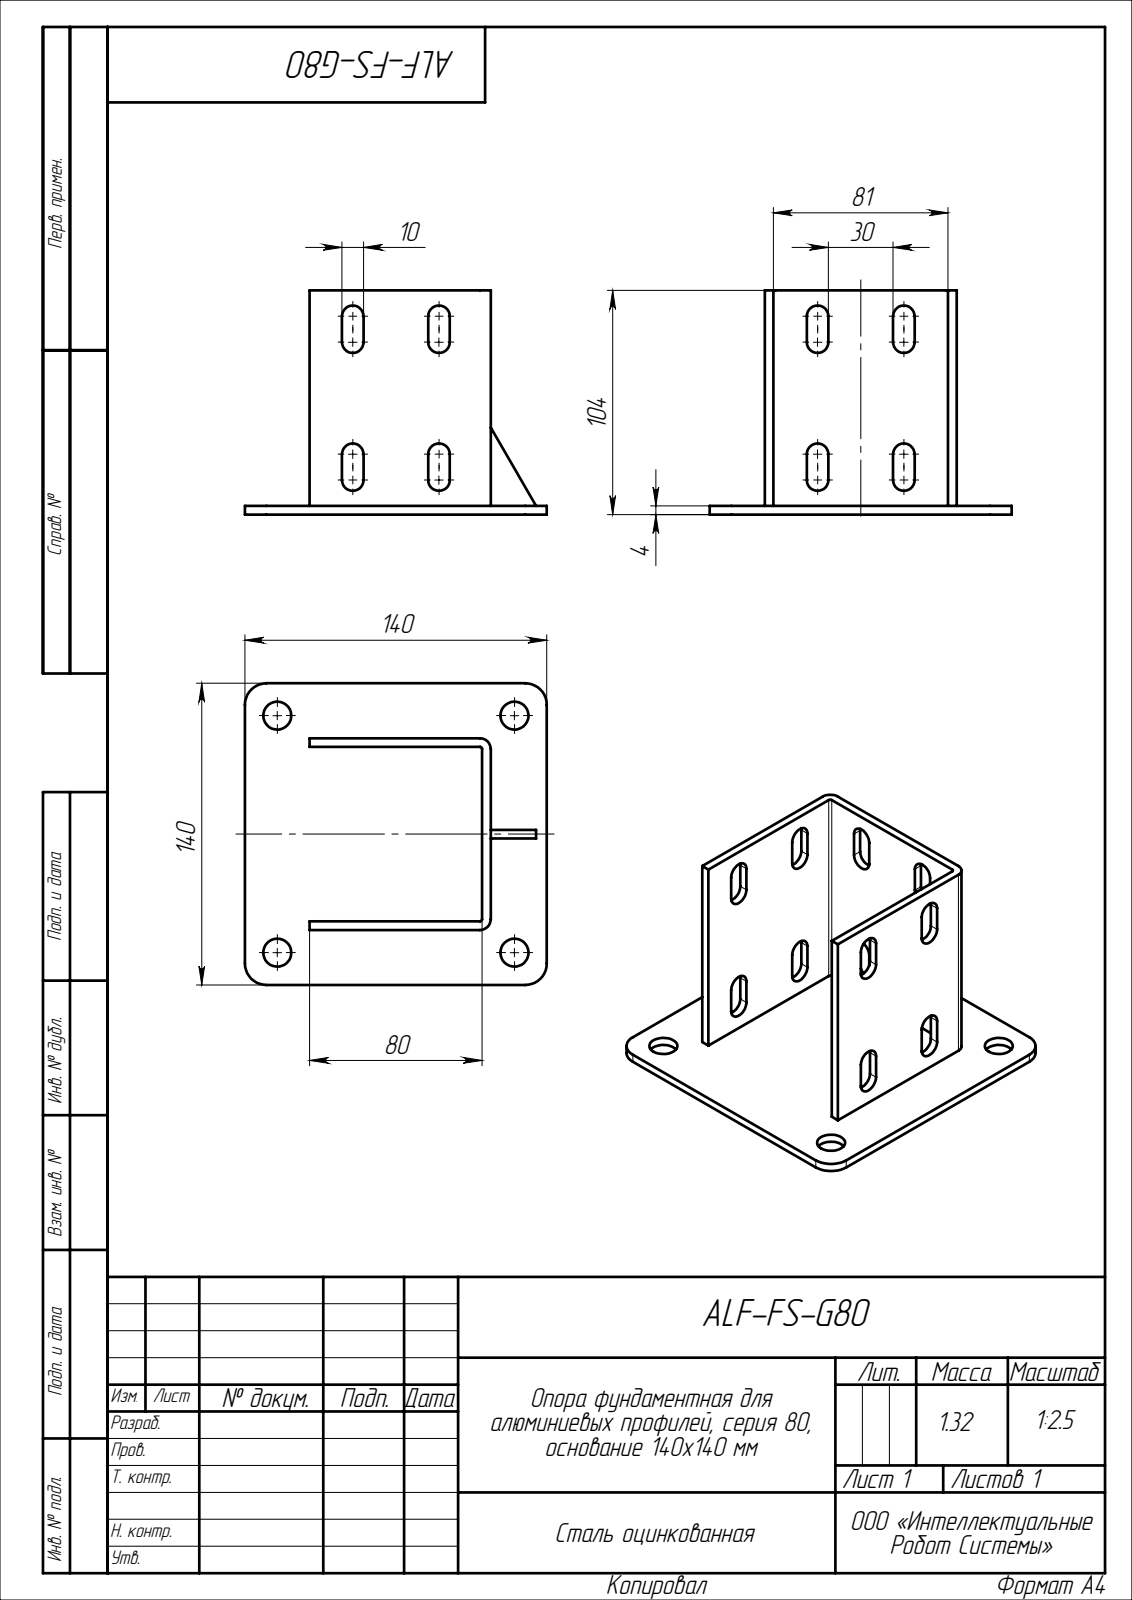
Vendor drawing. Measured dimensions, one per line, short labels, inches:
name: ALF-FS-G80
written by: SolidWorks 2022 (CONFIG_CONTROL_DESIGN)
unit: in
bodies: 1 solid, 82 faces (42 planar, 40 cylindrical, 0 other)
size: 5.512 × 5.512 × 4.094
volume: 10.16 in³; area: 138.7 in²
holes: 4× ⌀0.512
rounds: 18× R0.197, 4× R0.394, 2× R0.039
face distances: 0.157, 3.346, 3.189, 3.504, 1.673, 1.181, 1.004, 1.161, 4.094, 3.937
hole spacings: 4.331, 6.124
